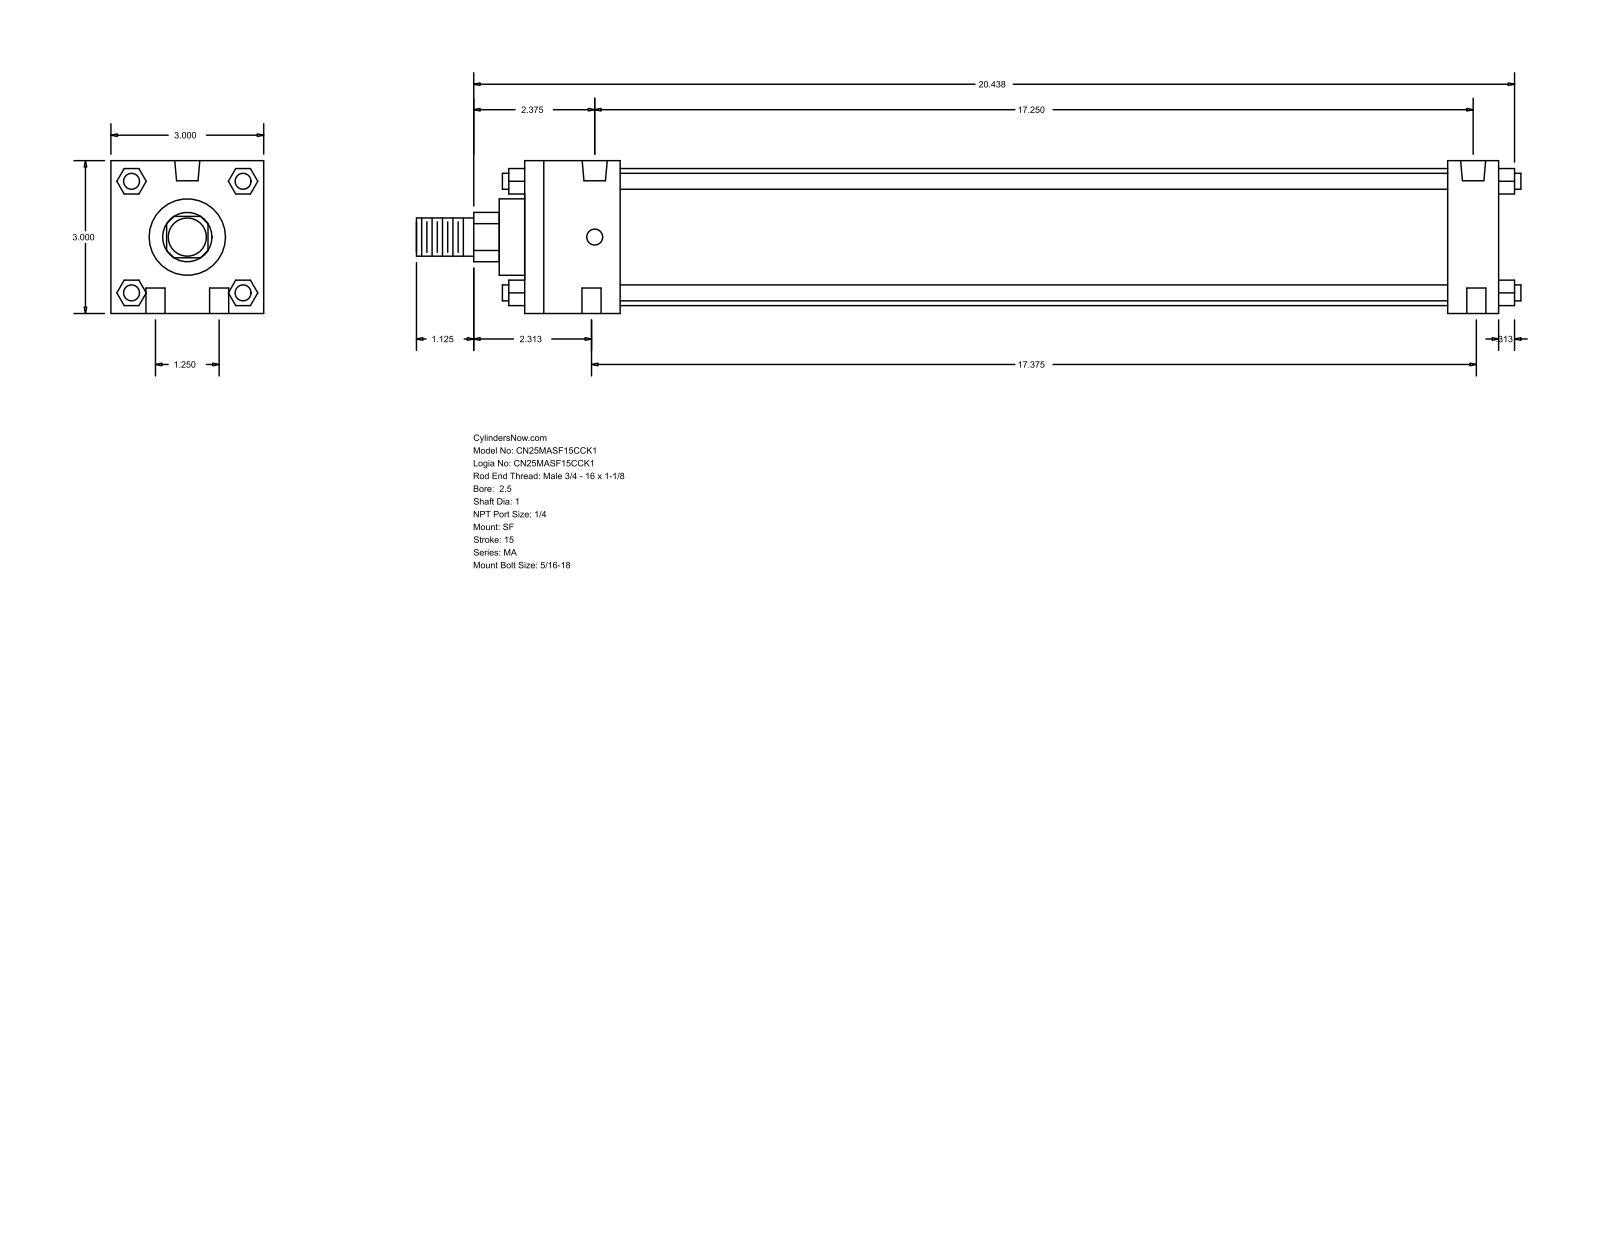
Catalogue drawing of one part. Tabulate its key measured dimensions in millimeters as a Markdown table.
| quantity | value |
| --- | --- |
| part name | MA_SF__0250_1 |
| STEP written by | GSSL Pune (CONFIG_CONTROL_DESIGN) |
| units | millimeters |
| bodies | 0 solids, 124 faces (94 planar, 30 cylindrical, 0 other) |
| overall size | 550.86 × 76.2 × 76.2 |
| round holes (diameter × count) | 9.53 × 4, 7.94 × 2, 12.49 × 2 |
| round bosses / shafts (diameter × count) | 7.94 × 4, 68.33 × 1, 38.1 × 1, 25.4 × 1, 19.05 × 1 |
| partial cylindrical surfaces (radius × count) | 12.29 × 1 |
| main face-to-face distances | 76.2, 485.78, 12.7, 460.37, 25.41, 47.63, 412.74, 438.15, 27.81, 48.17 |
| hole center spacings | 15.96, 31.76, 438.15, 440.02, 440.03, 441.32, 442.46 |
